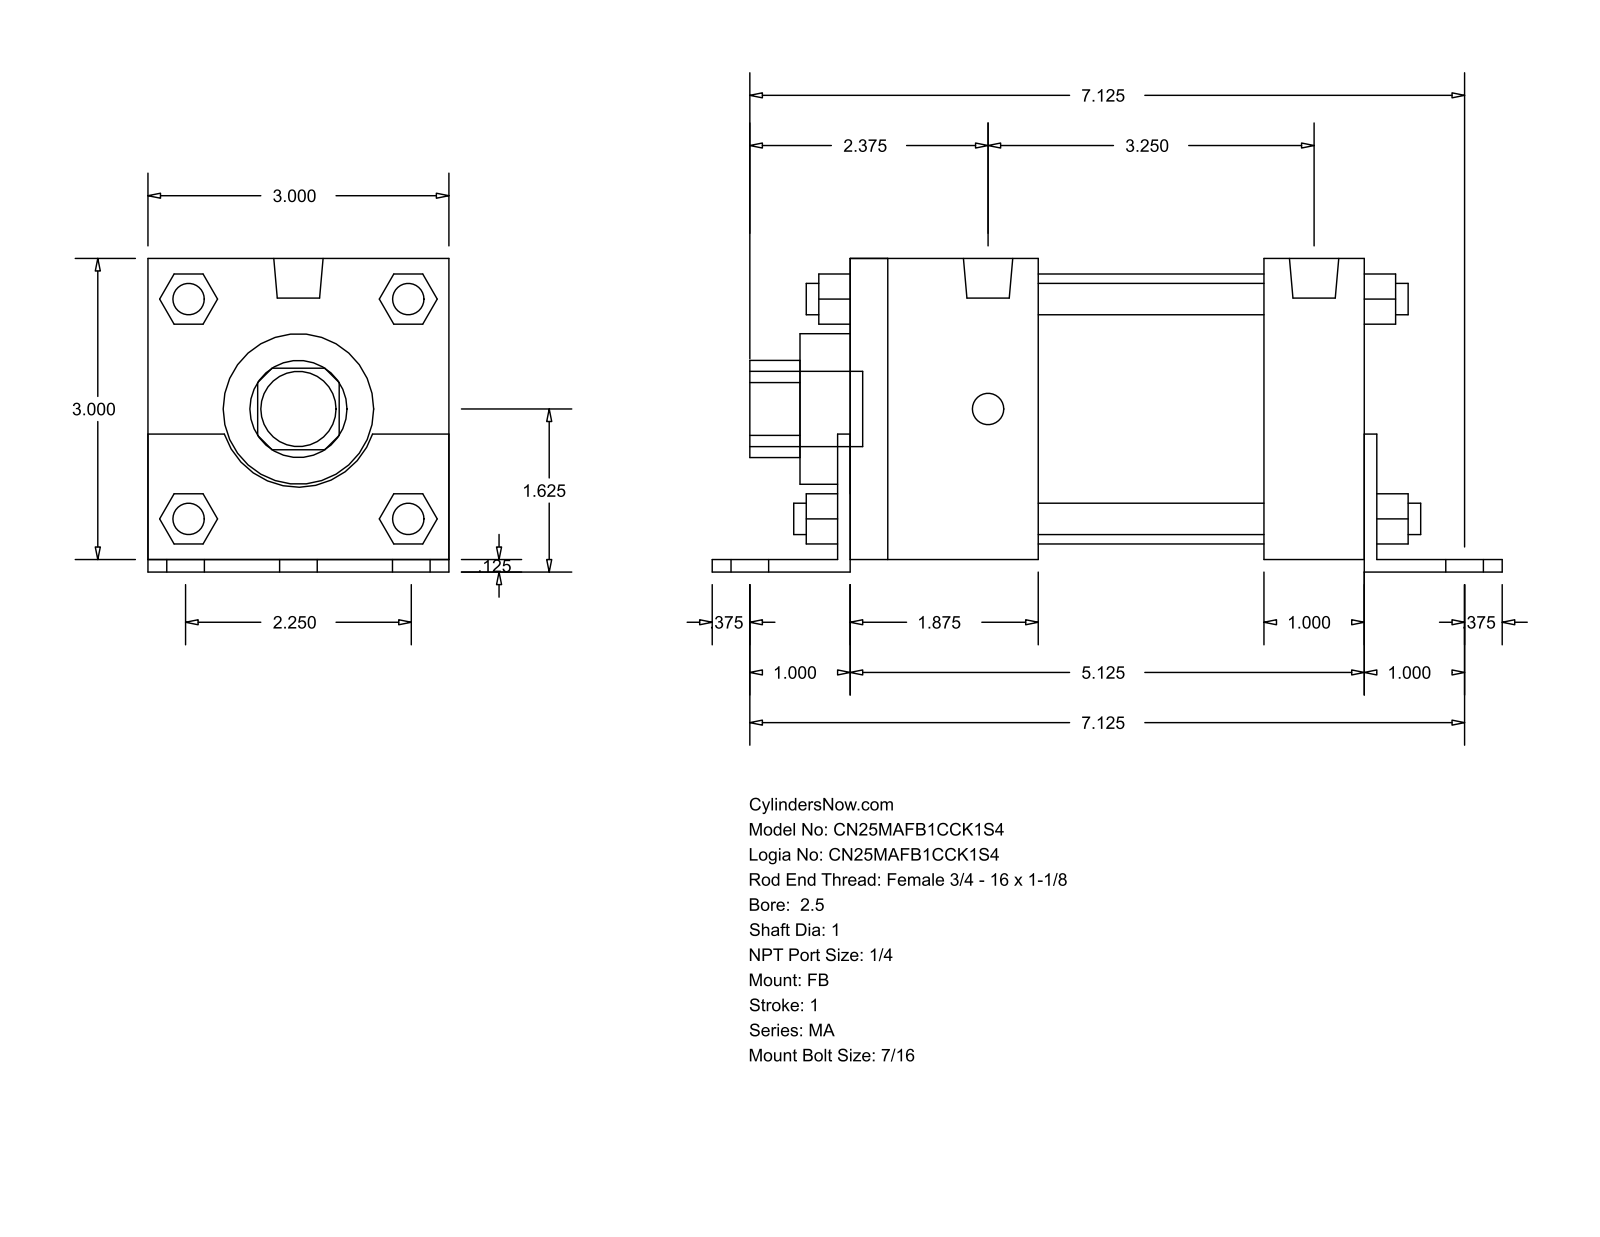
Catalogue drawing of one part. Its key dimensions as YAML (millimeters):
part_name: "MA_FB__0250_1"
step_written_by: "GSSL Pune (CONFIG_CONTROL_DESIGN)"
units: millimeters
bodies: {solids: 0, faces: 140, planar: 105, cylindrical: 35, other: 0}
overall_size: [200.03, 79.38, 76.2]
round_holes:
  - {diameter: 25.4, count: 1}
  - {diameter: 38.1, count: 1}
  - {diameter: 68.33, count: 1}
round_bosses_or_shafts:
  - {diameter: 7.94, count: 8}
  - {diameter: 11.11, count: 6}
  - {diameter: 12.49, count: 2}
  - {diameter: 19.05, count: 1}
partial_cylinders:
  - {radius: 12.29, count: 1}
  - {radius: 19.81, count: 1}
face_to_face_distances: [76.2, 3.17, 79.37, 130.17, 3.18, 12.7, 133.35, 28.57, 47.63, 82.54]
